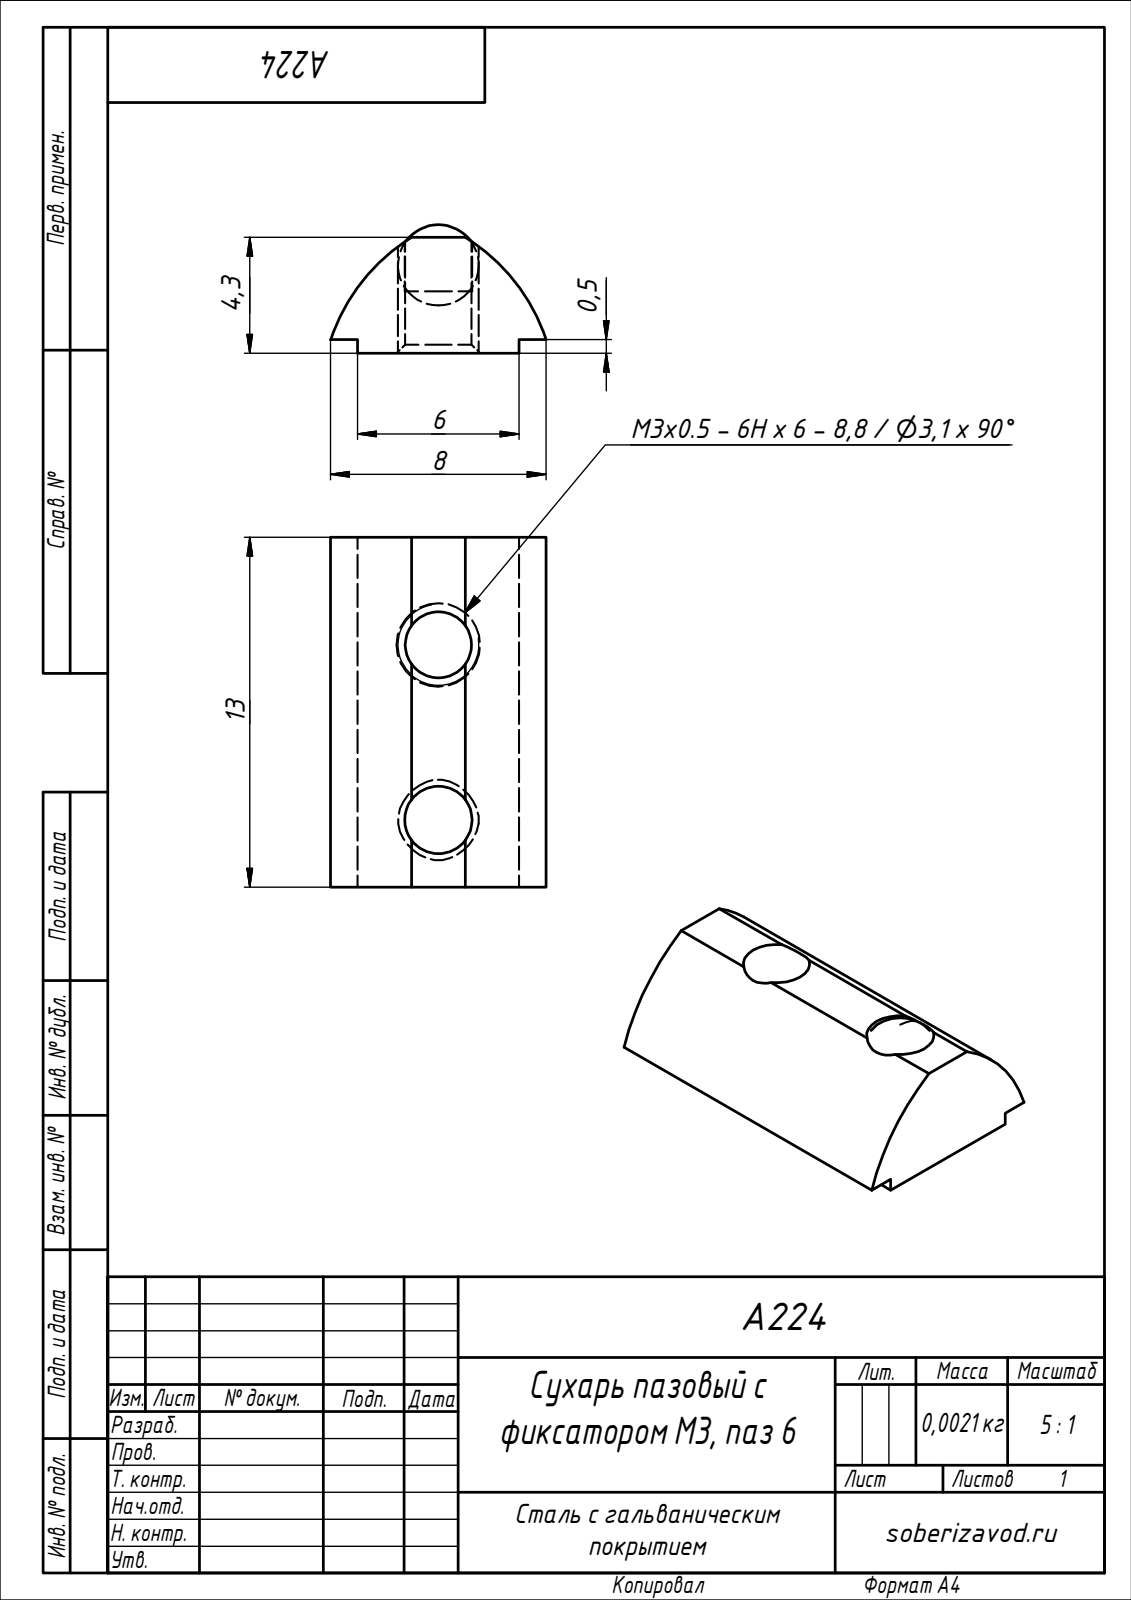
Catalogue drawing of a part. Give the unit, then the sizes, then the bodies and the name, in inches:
Units: inches
Overall size (bounding box): 0.512 × 0.315 × 0.188
Round holes (diameter × count): ⌀0.097 ×1, ⌀0.098 ×1
Partial cylindrical surfaces — rounded edges, fillets, slot ends (radius × count): R0.28 ×2
Main face-to-face distances: 0.02, 0.512, 0.169, 0.15, 0.236, 0.091, 0.071, 0.079
Hole centre spacings: 0.256
Volume: 0.019 in³ · Surface area: 0.598 in²
Bodies: 2 solids, 17 faces (11 planar, 4 cylindrical, 2 other)
Part name (STEP PRODUCT): A224
STEP written by: Autodesk Inventor 2018 (AP242_MANAGED_MODEL_BASED_3D_ENGINEERING_MIM_LF)
